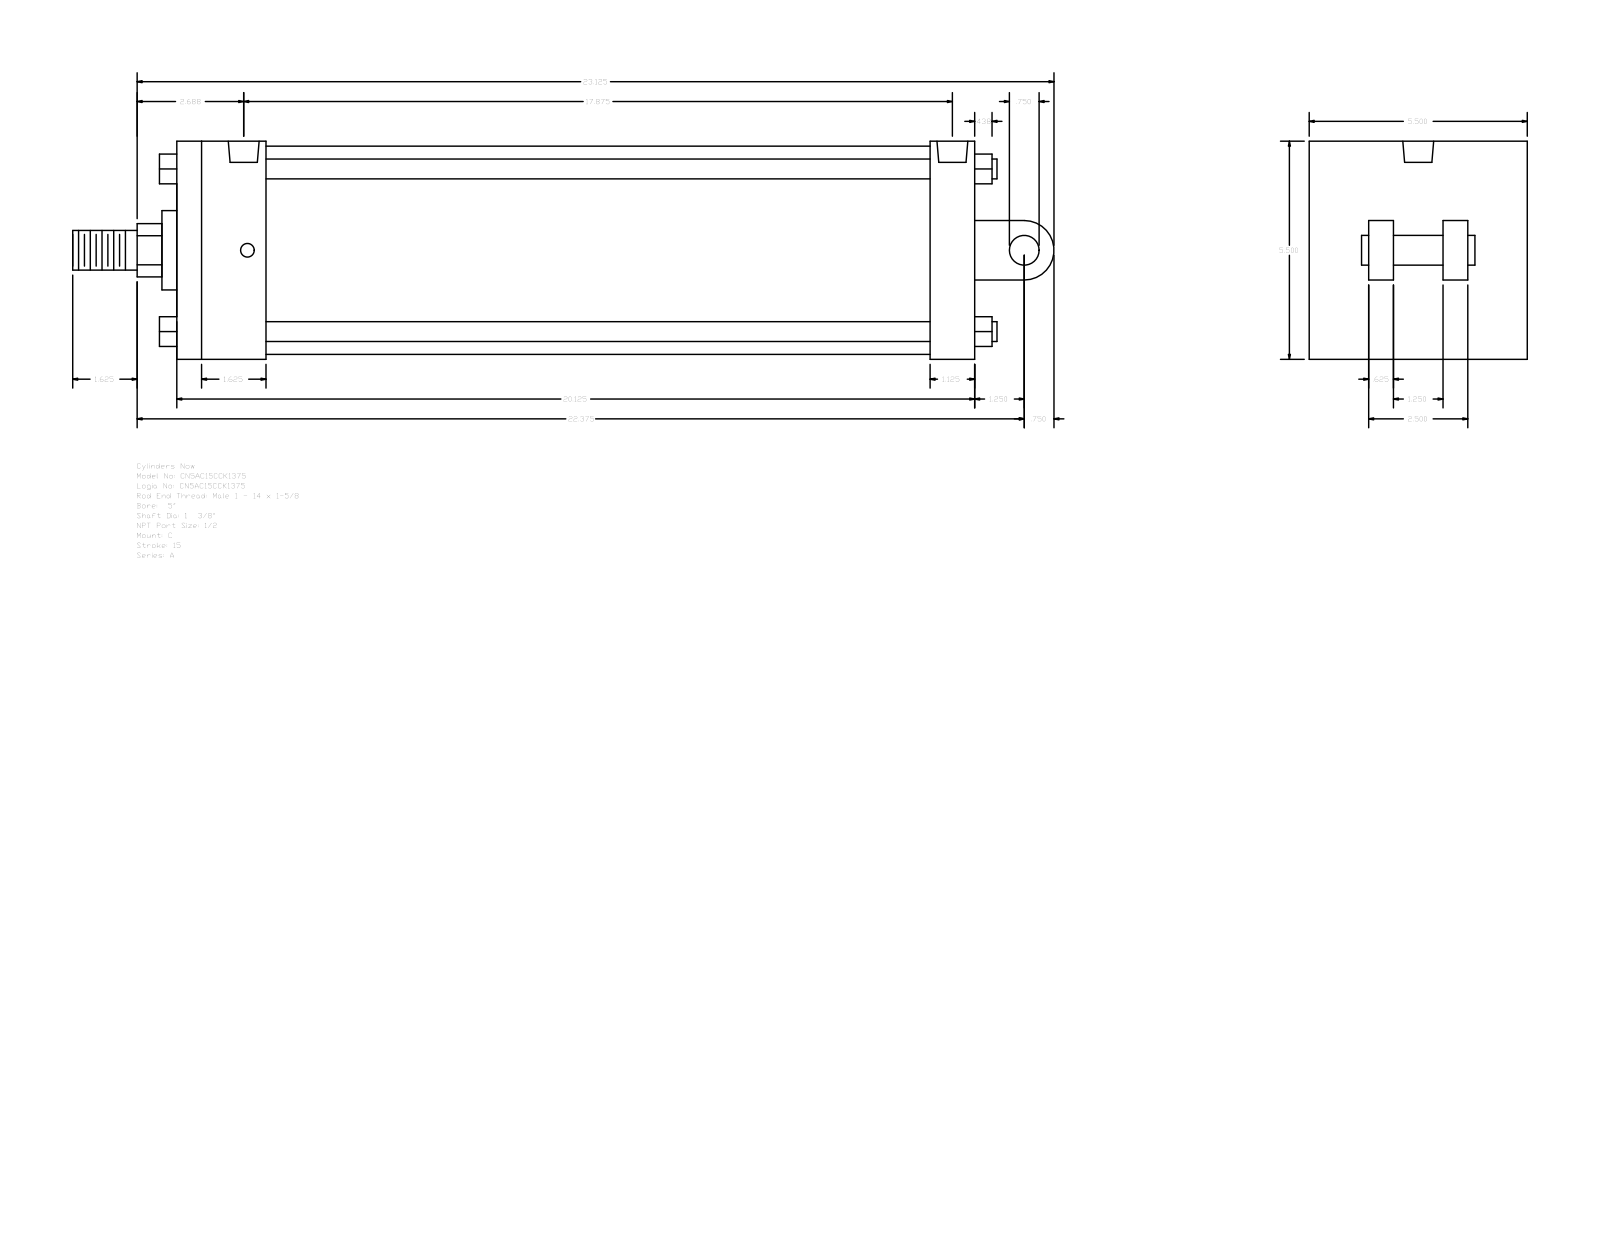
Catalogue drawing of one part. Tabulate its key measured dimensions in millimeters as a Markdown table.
| quantity | value |
| --- | --- |
| part name | A_C__0500_1.375 |
| STEP written by | GSSL Pune (CONFIG_CONTROL_DESIGN) |
| units | millimeters |
| bodies | 0 solids, 135 faces (102 planar, 33 cylindrical, 0 other) |
| overall size | 628.65 × 139.7 × 139.7 |
| round holes (diameter × count) | 8.73 × 4, 19.77 × 2 |
| round bosses / shafts (diameter × count) | 12.7 × 4, 133.35 × 1, 50.8 × 1, 34.92 × 1, 25.4 × 1, 19.05 × 1 |
| partial cylindrical surfaces (radius × count) | 17.06 × 1, 19.05 × 1 |
| main face-to-face distances | 139.7, 511.18, 57.15, 28.58, 482.6, 425.45, 454.03, 38.1, 53.97, 85.73 |
| hole center spacings | 2.39, 449.25, 451.64, 454.03 |
